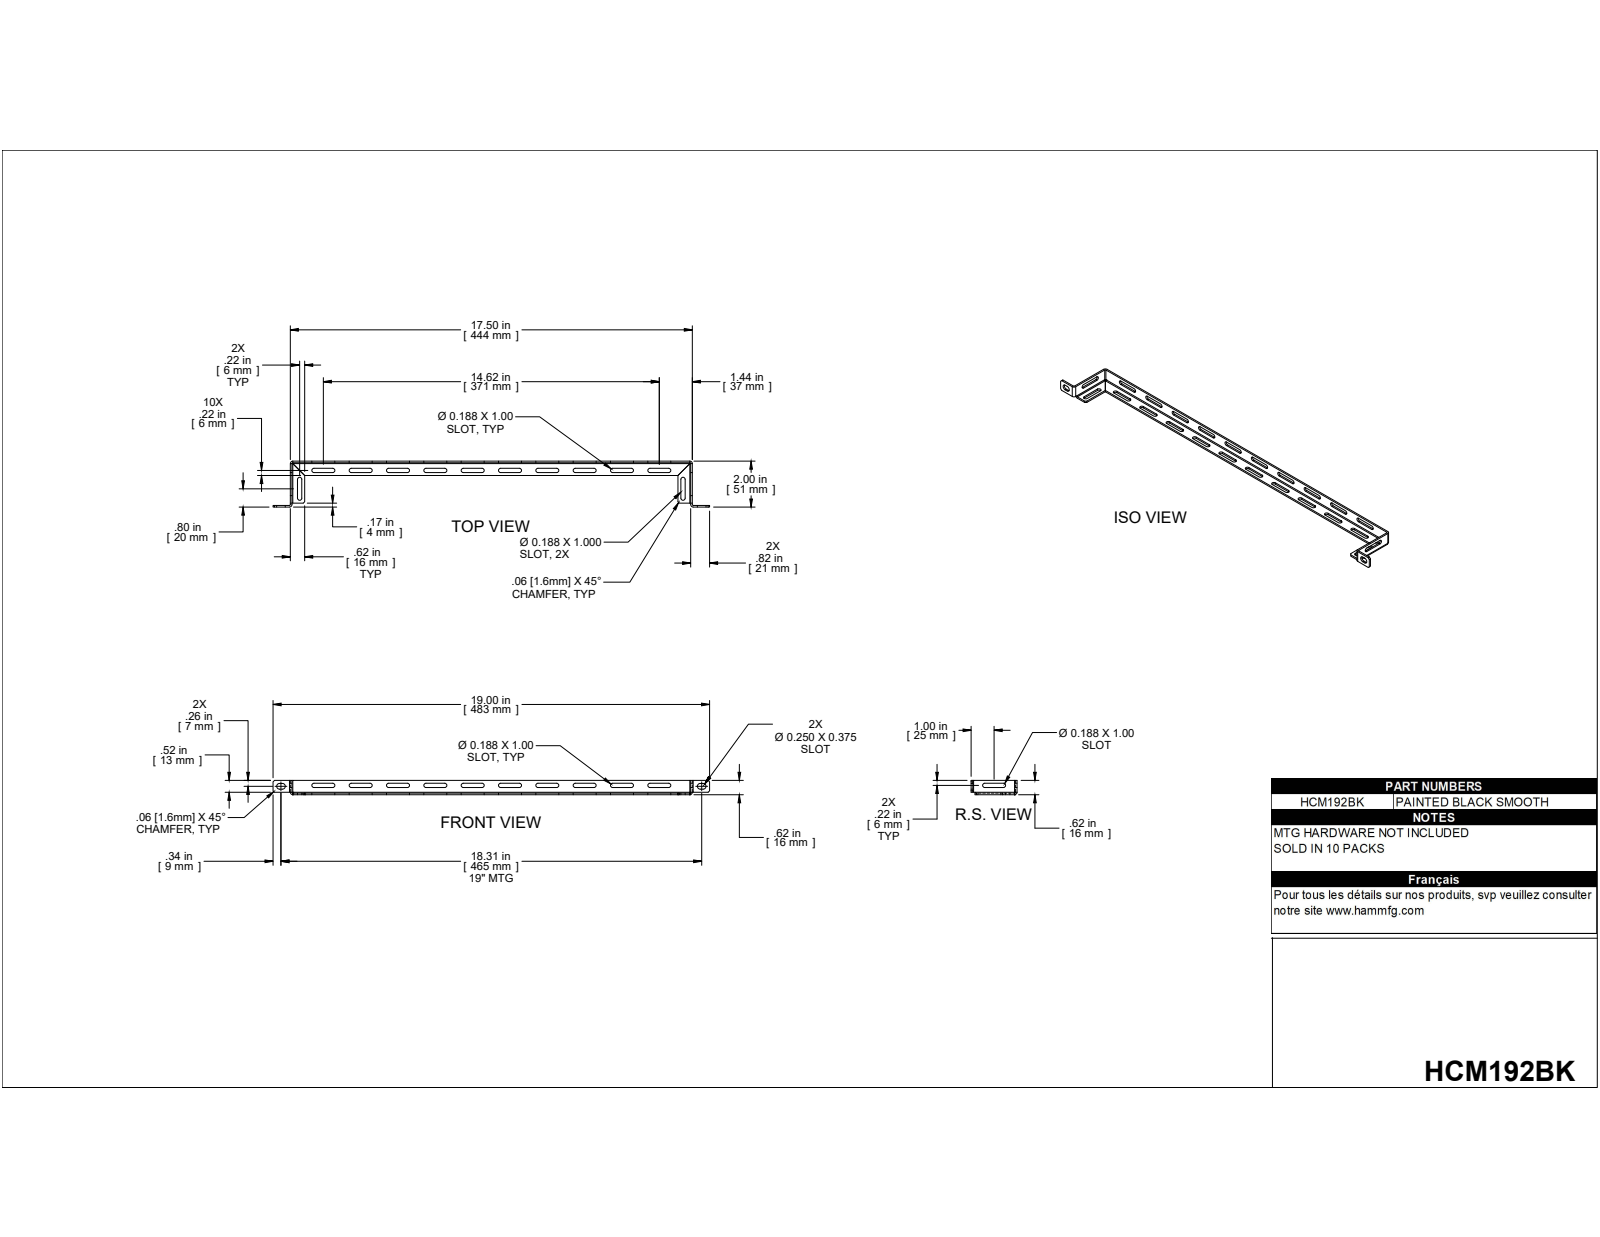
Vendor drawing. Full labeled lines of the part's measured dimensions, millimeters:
Part name (STEP PRODUCT): COM57141-2
STEP written by: ST-DEVELOPER v16.7 (AUTOMOTIVE_DESIGN)
Units: millimetres
Bodies: 1 solid, 164 faces (94 planar, 66 cylindrical, 4 other)
Overall size (bounding box): 482.6 × 50.8 × 15.88
Volume: 23 355 mm³ · Surface area: 30 374 mm²
Partial cylindrical surfaces — rounded edges, fillets, slot ends (radius × count): R2.38 ×44, R0.91 ×7, R2.74 ×7, R3.17 ×4, R2.38 ×2
Main face-to-face distances: 1.83, 7.94, 14.04, 15.87, 442.67, 6.11, 10.86, 12.69, 4.75, 15.88
